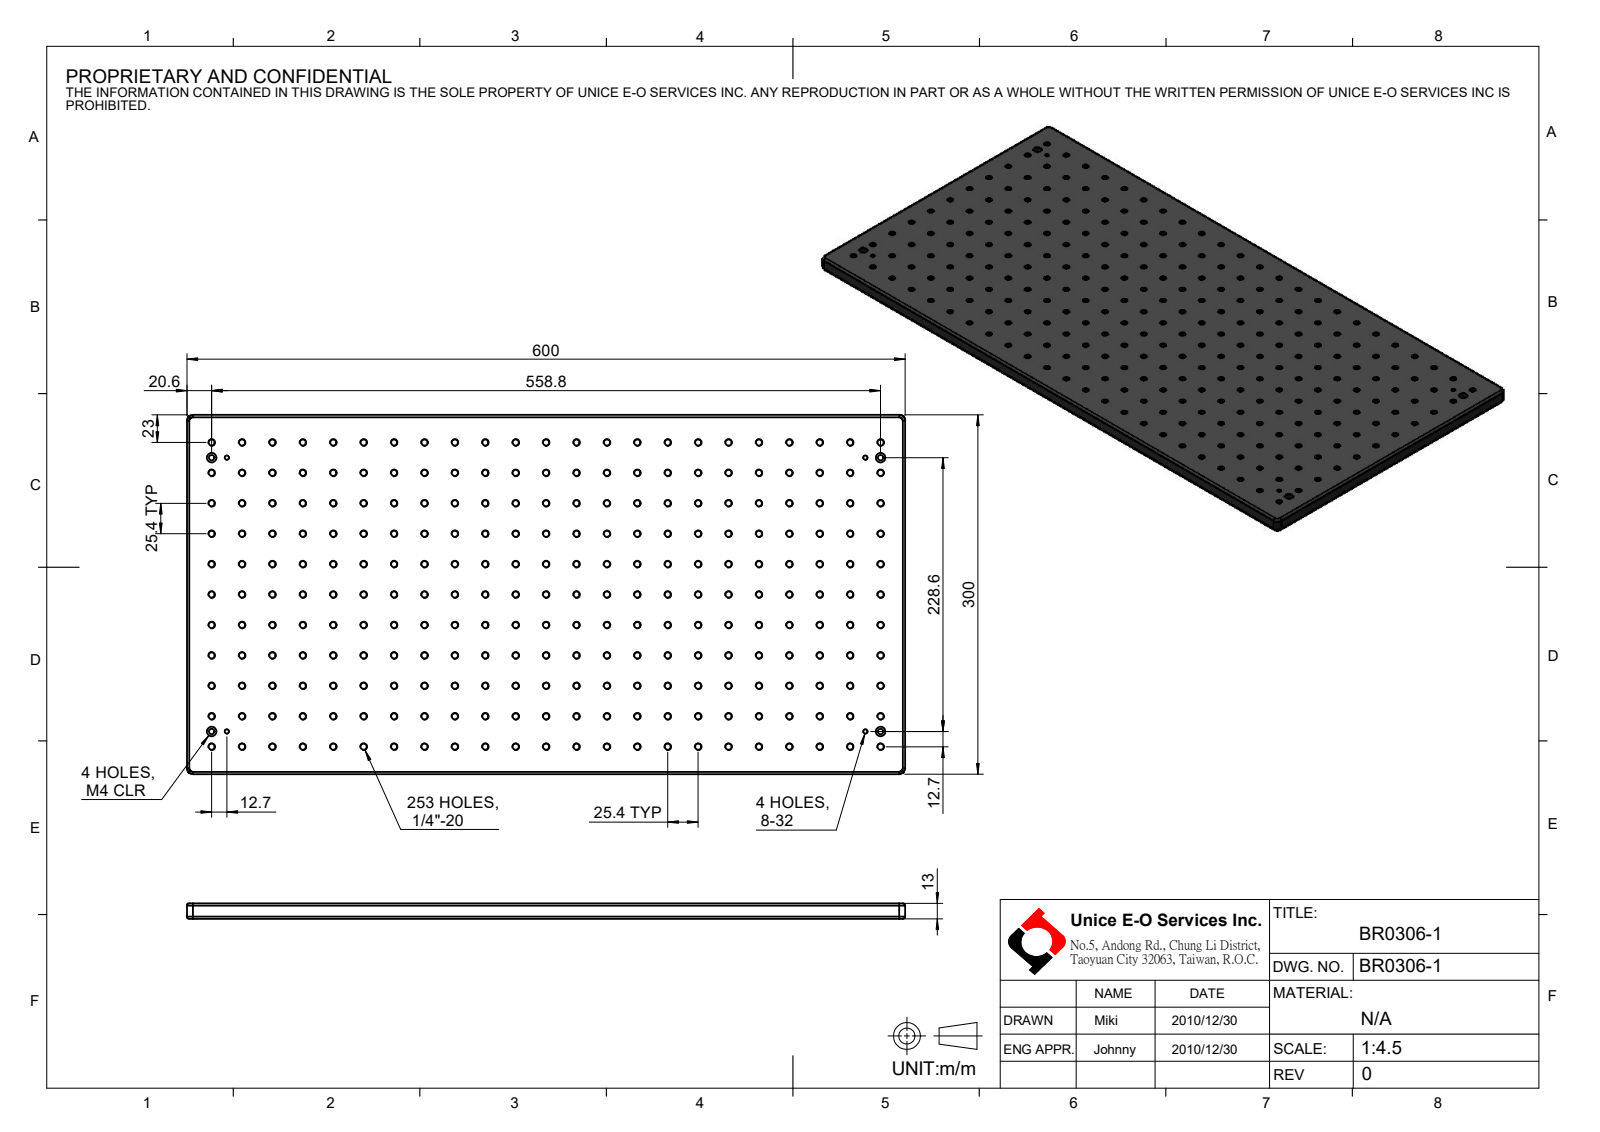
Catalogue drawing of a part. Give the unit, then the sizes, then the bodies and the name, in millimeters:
Units: millimetres
Overall size (bounding box): 600 × 300 × 13
Round holes (diameter × count): ⌀5.11 ×253, ⌀3.45 ×4, ⌀4.5 ×4, ⌀8 ×4
Partial cylindrical surfaces — rounded edges, fillets, slot ends (radius × count): R2 ×8, R5 ×4
Main face-to-face distances: 13, 300, 600, 7, 6
Hole centre spacings: 25.4, 50.8, 76.2, 101.6, 127, 228.6, 152.4, 177.8
Volume: 2 267 000 mm³ · Surface area: 423 922 mm²
Bodies: 1 solid, 560 faces (10 planar, 542 cylindrical, 8 other)
Part name (STEP PRODUCT): BR0306-1
STEP written by: SolidWorks 2016 (CONFIG_CONTROL_DESIGN)
